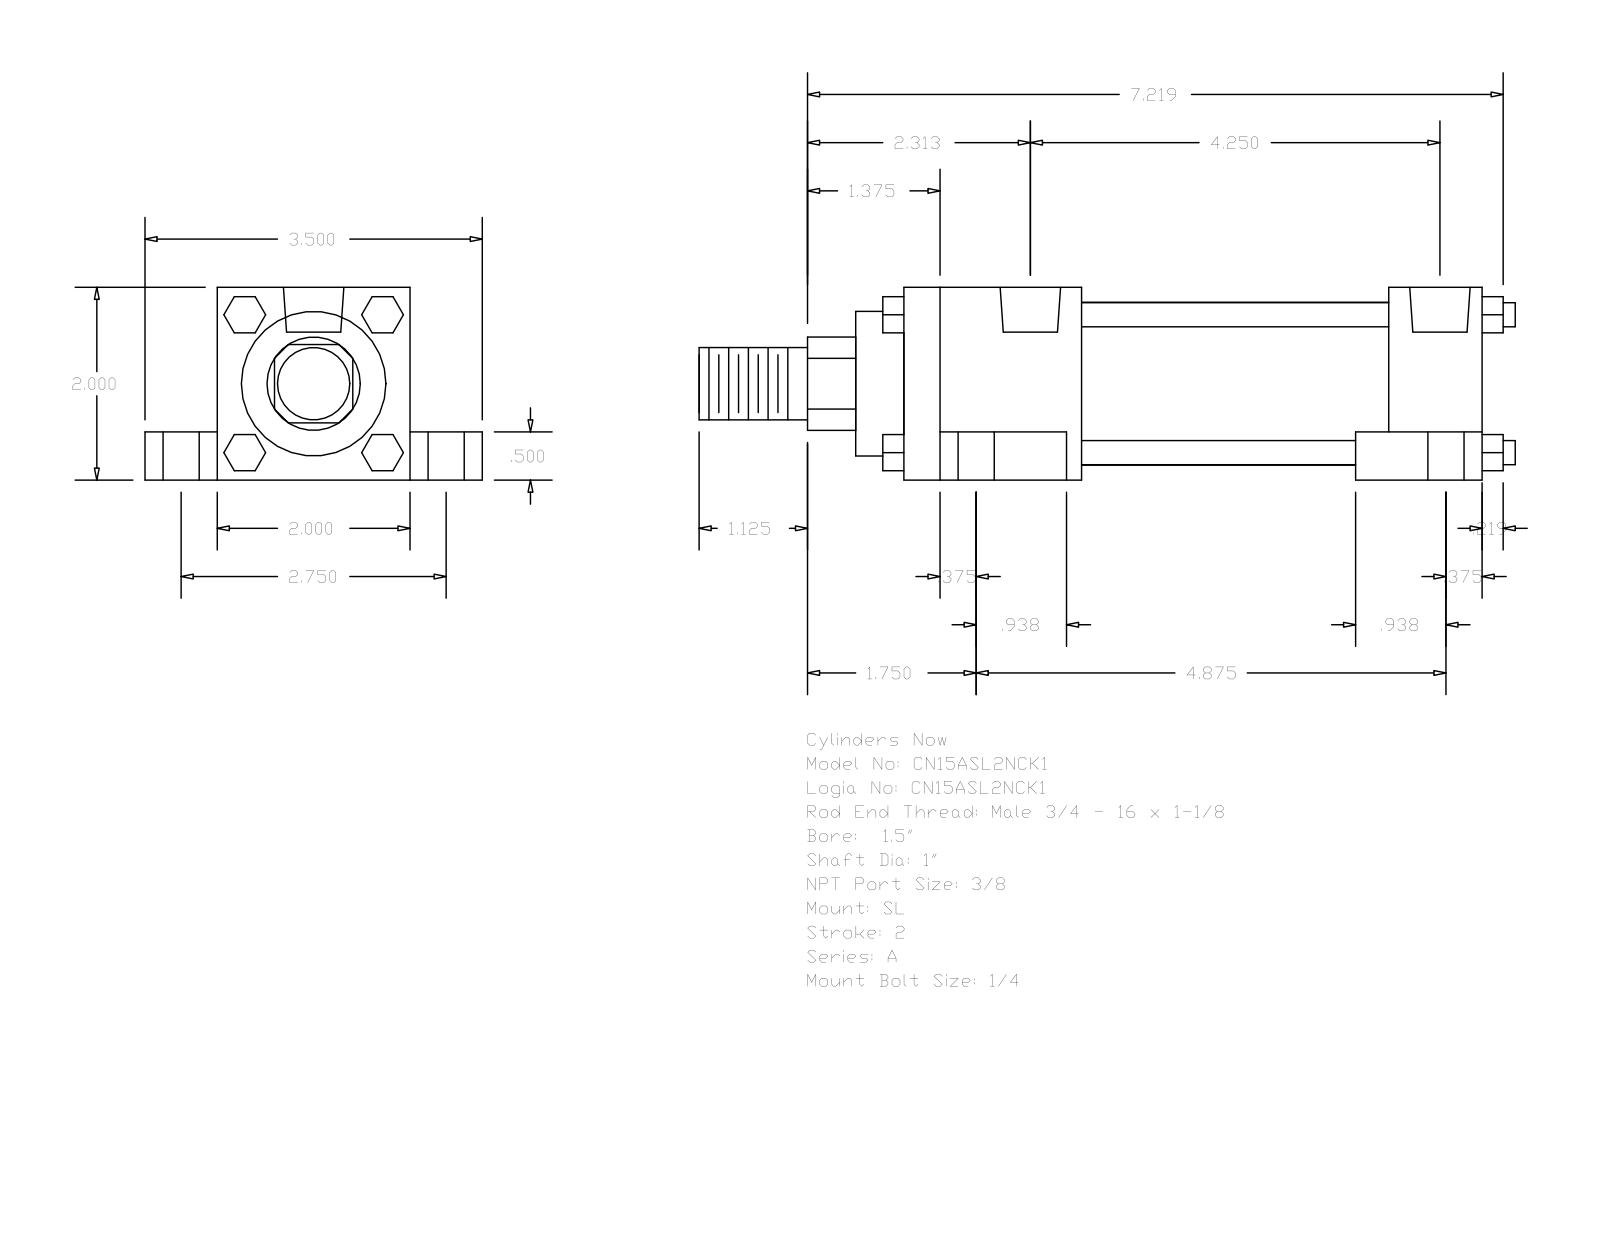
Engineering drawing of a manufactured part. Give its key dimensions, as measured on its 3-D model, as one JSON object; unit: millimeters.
{"part_name": "A_SL__0150_1", "step_written_by": "GSSL Pune (CONFIG_CONTROL_DESIGN)", "units": "millimeters", "bodies": {"solids": 0, "faces": 148, "planar": 112, "cylindrical": 36, "other": 0}, "overall_size": [215.11, 88.9, 50.8], "round_holes": [[5.56, 4], [9.53, 4], [15.88, 4], [15.93, 2]], "round_bosses_or_shafts": [[6.35, 4], [42.93, 1], [38.1, 1], [25.4, 1], [19.05, 1]], "partial_cylinders_radius": [[12.29, 1]], "face_to_face_distances": [50.8, 12.7, 38.1, 19.05, 69.85, 9.52, 152.4, 33.34, 127.79, 24.61], "hole_center_spacings": [3.97, 34.96, 35.36, 37.73, 39.41, 69.84, 100.01, 103.98]}
